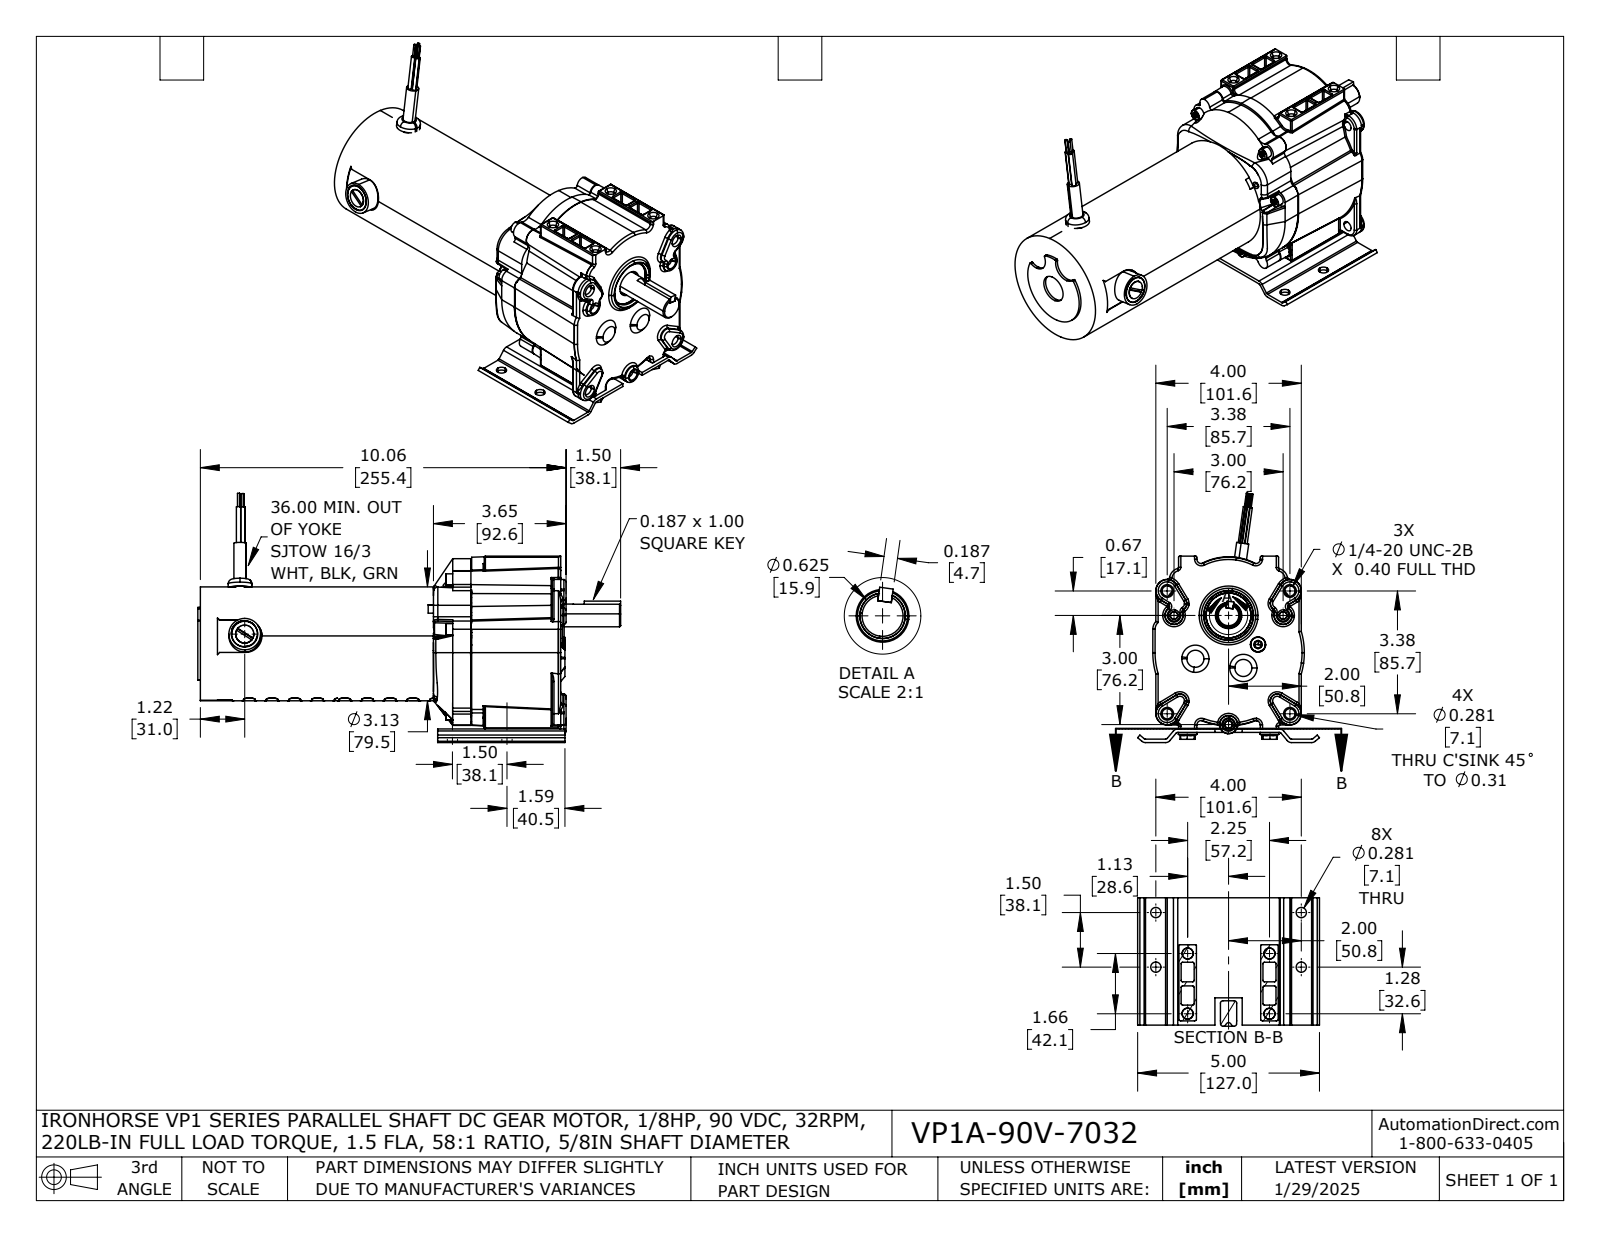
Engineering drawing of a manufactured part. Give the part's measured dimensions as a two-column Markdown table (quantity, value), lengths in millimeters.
| quantity | value |
| --- | --- |
| part name | VP1A-90V-7032 |
| STEP written by | SolidWorks 2024 (AUTOMOTIVE_DESIGN) |
| units | millimeters |
| bodies | 10 solids, 2472 faces (654 planar, 701 cylindrical, 1117 other) |
| overall size | 295.3 × 174.1 × 127 |
| volume | 1 621 000 mm³ |
| surface area | 222 800 mm² |
| round holes (diameter × count) | 7.1 × 12, 5.5 × 5, 4 × 3, 5.3 × 3, 3.4 × 2, 4.2 × 2, 5.2 × 2, 10.1 × 2, 17.5 × 2, 22.2 × 2, 19.1 × 1, 20.7 × 1 |
| round bosses / shafts (diameter × count) | 7.8 × 5, 4.8 × 5, 13 × 4, 7.6 × 4, 3 × 3, 1.5 × 3, 22.2 × 2, 18.6 × 2 |
| partial cylindrical surfaces (radius × count) | 0.8 × 52, 0.8 × 38, 1.6 × 23, 3 × 18, 4 × 18, 4.8 × 10, 3.8 × 9, 4.1 × 9 |
| main face-to-face distances | 2.4, 62.2, 88.9, 26.7, 239.8, 177.6, 150.9, 11.9, 177, 251.7 |
| hole center spacings | 38.1, 85.7, 43, 12.5, 17.7, 31.1, 36.2, 39.4 |
